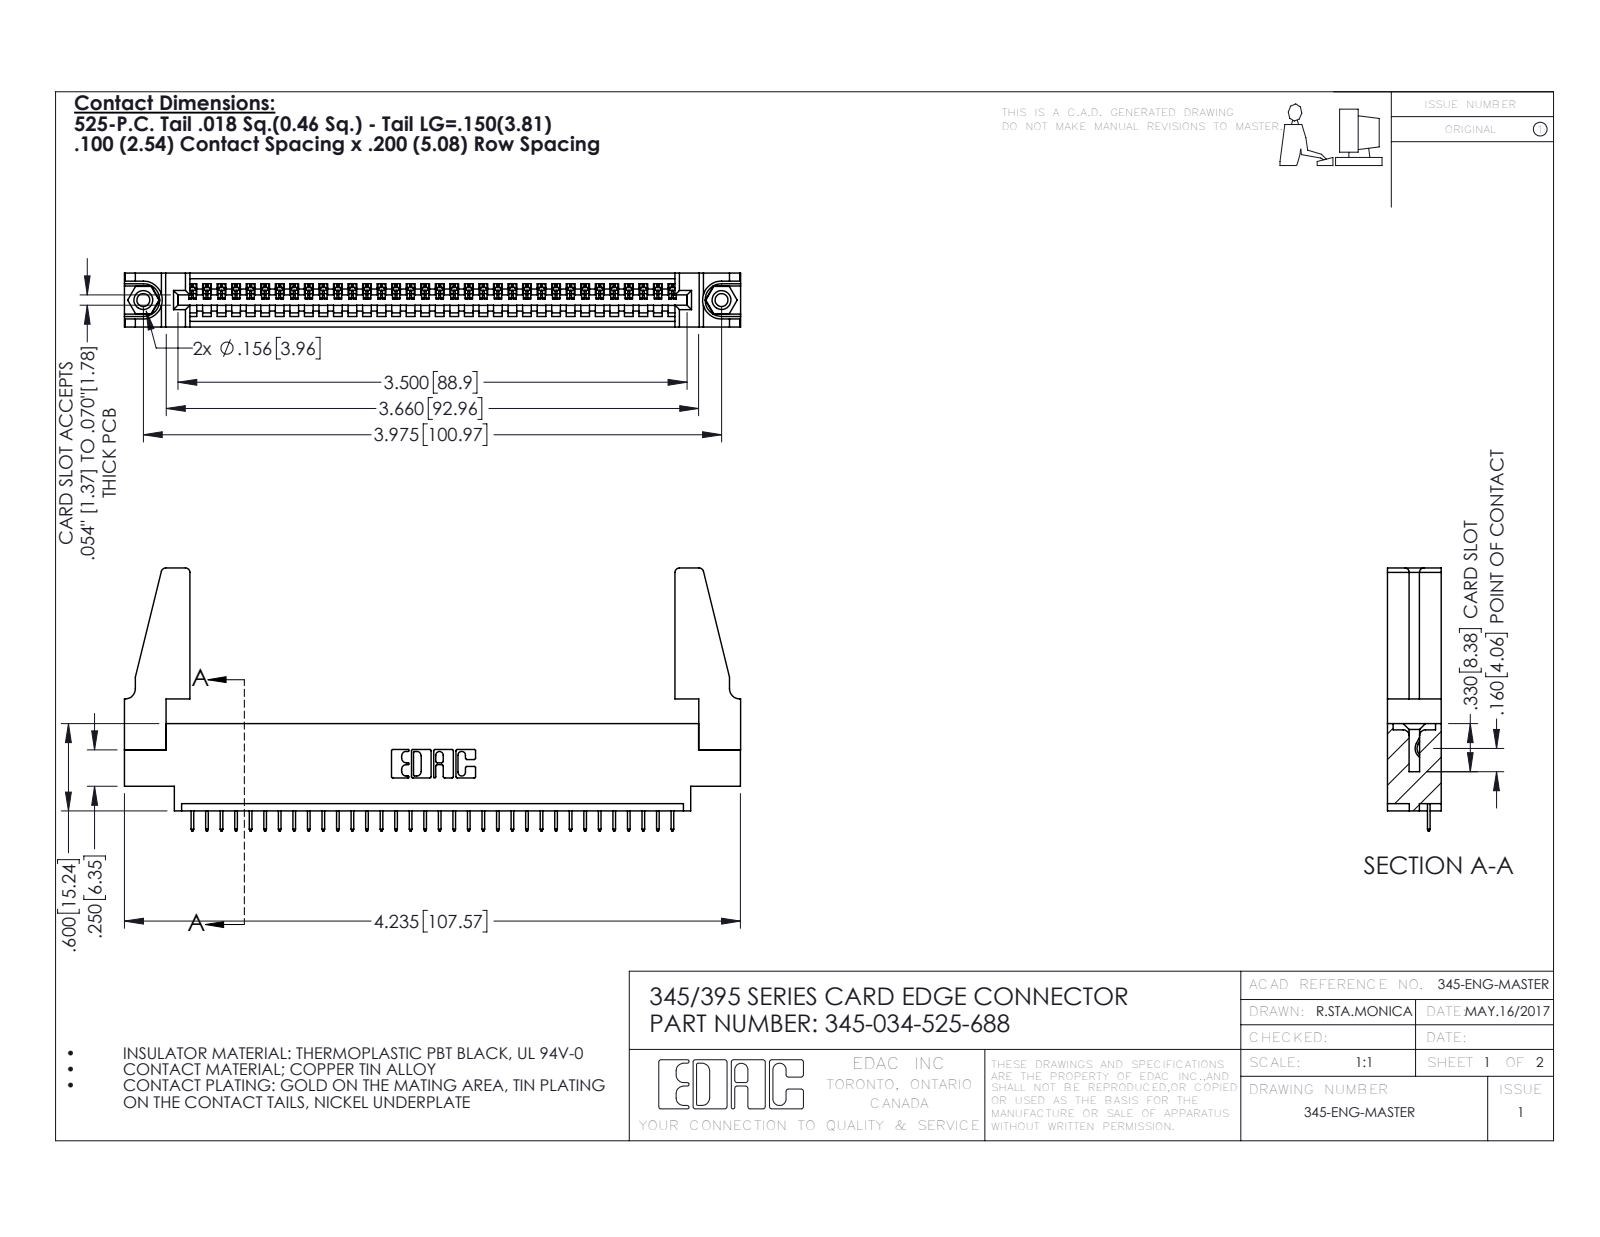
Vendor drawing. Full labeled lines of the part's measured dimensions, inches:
Part name (STEP PRODUCT): 345-034-525-688; 345-250-001_345-250-001-102; 345-292-001_345-293-125; 345 Part_0.170 Offset - 0.156 Dia-TH (+1 more)
STEP written by: SolidWorks 2020 (CONFIG_CONTROL_DESIGN)
Units: inches
Bodies: 39 solids, 2362 faces (1720 planar, 626 cylindrical, 16 other)
Overall size (bounding box): 4.236 × 1.807 × 0.37
Volume: 0.803 in³ · Surface area: 24.56 in²
Round holes (diameter × count): ⌀0.089 ×2, ⌀0.125 ×2, ⌀0.156 ×2, ⌀0.064 ×1
Round bosses / shafts (diameter × count): ⌀0.155 ×2
Partial cylindrical surfaces — rounded edges, fillets, slot ends (radius × count): R0.006 ×68, R0.01 ×22, R0.03 ×8, R0.007 ×6, R0.031 ×6, R0.026 ×3, R0.031 ×2, R0.04 ×2
Main face-to-face distances: 0.37, 0.072, 0.298, 0.2, 0.098, 0.272, 0.025, 0.225, 0.175, 0.072
Hole centre spacings: 0.27, 3.74, 3.975
